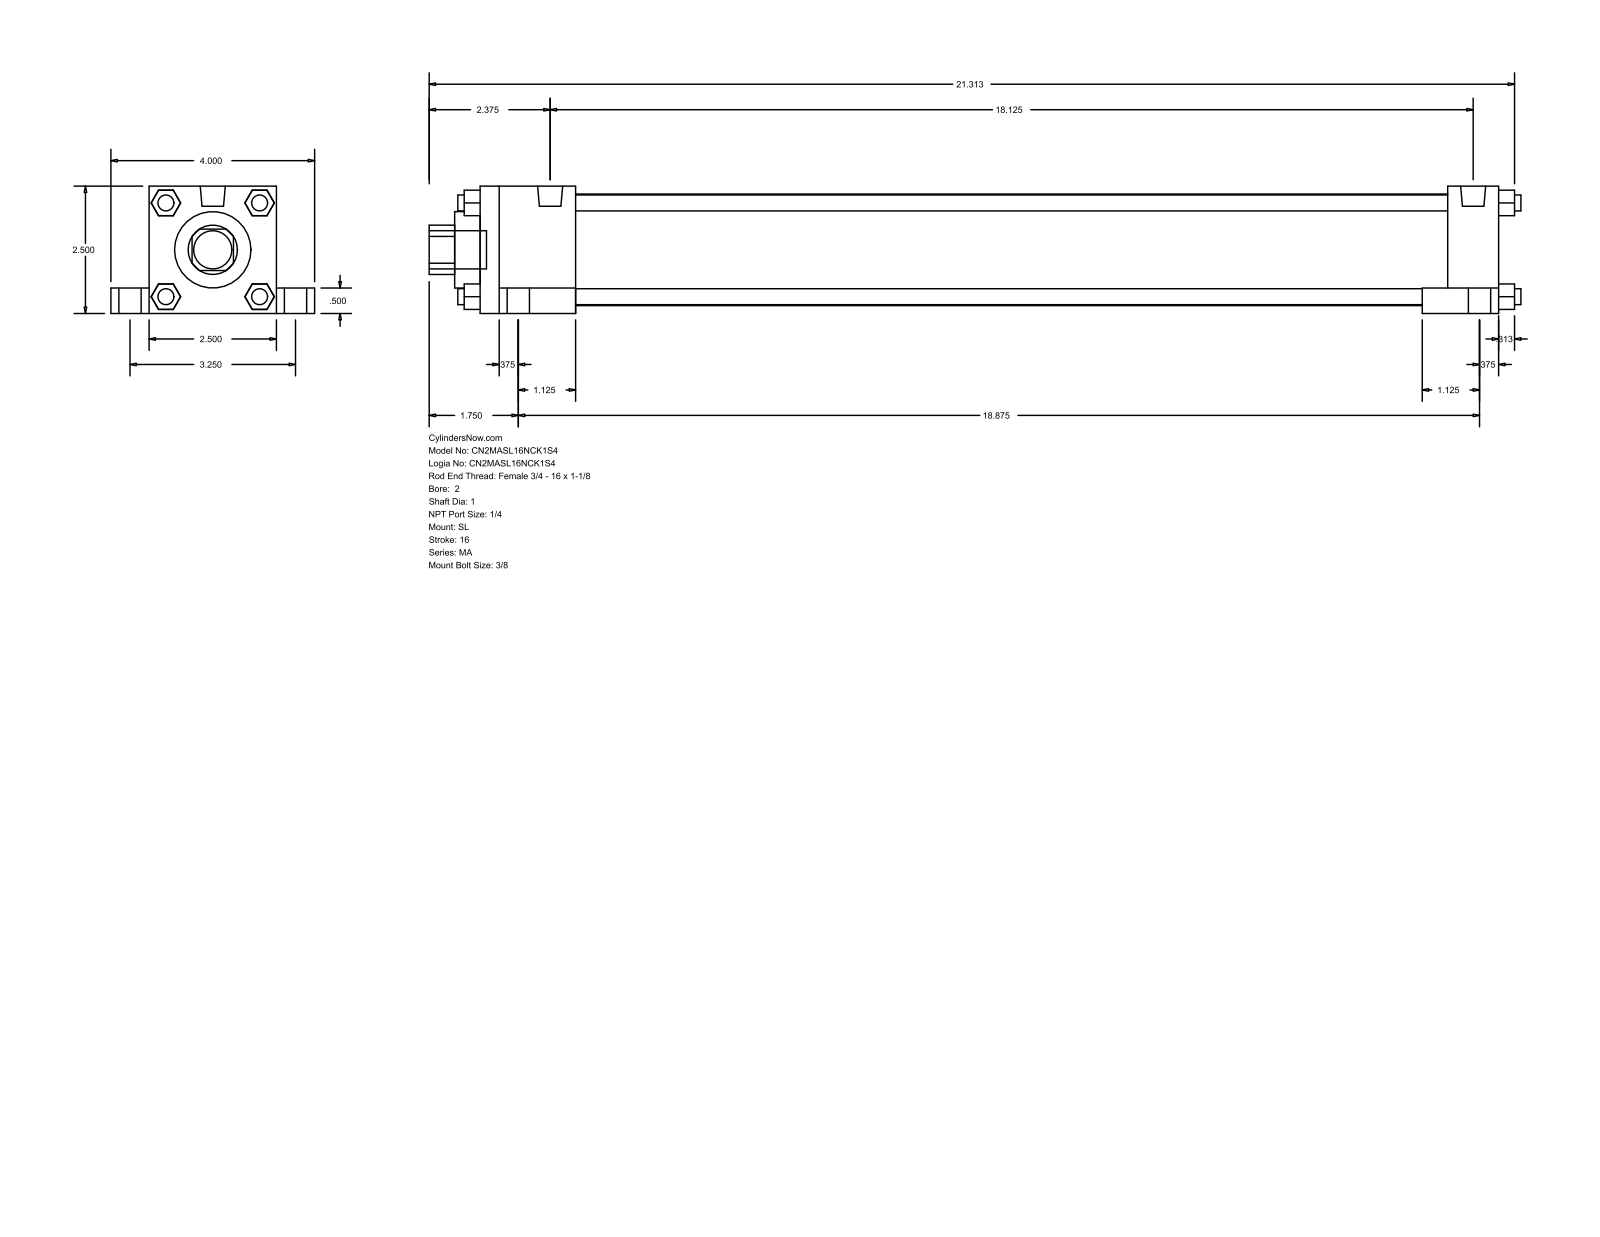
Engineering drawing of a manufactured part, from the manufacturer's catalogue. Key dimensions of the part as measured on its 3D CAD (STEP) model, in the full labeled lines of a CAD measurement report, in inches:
Part name (STEP PRODUCT): MA_SL__0200_1
STEP written by: GSSL Pune (CONFIG_CONTROL_DESIGN)
Units: inches
Bodies: 0 solids, 148 faces (112 planar, 36 cylindrical, 0 other)
Overall size (bounding box): 21.437 × 4 × 2.5
Round holes (diameter × count): ⌀1 ×1, ⌀1.5 ×1, ⌀2.19 ×1
Round bosses / shafts (diameter × count): ⌀0.313 ×8, ⌀0.687 ×4, ⌀0.437 ×4, ⌀0.492 ×2, ⌀0.75 ×1
Partial cylindrical surfaces — rounded edges, fillets, slot ends (radius × count): R0.484 ×1
Main face-to-face distances: 2.5, 0.5, 20, 0.75, 3.25, 1, 2, 1.875, 18.125, 19
